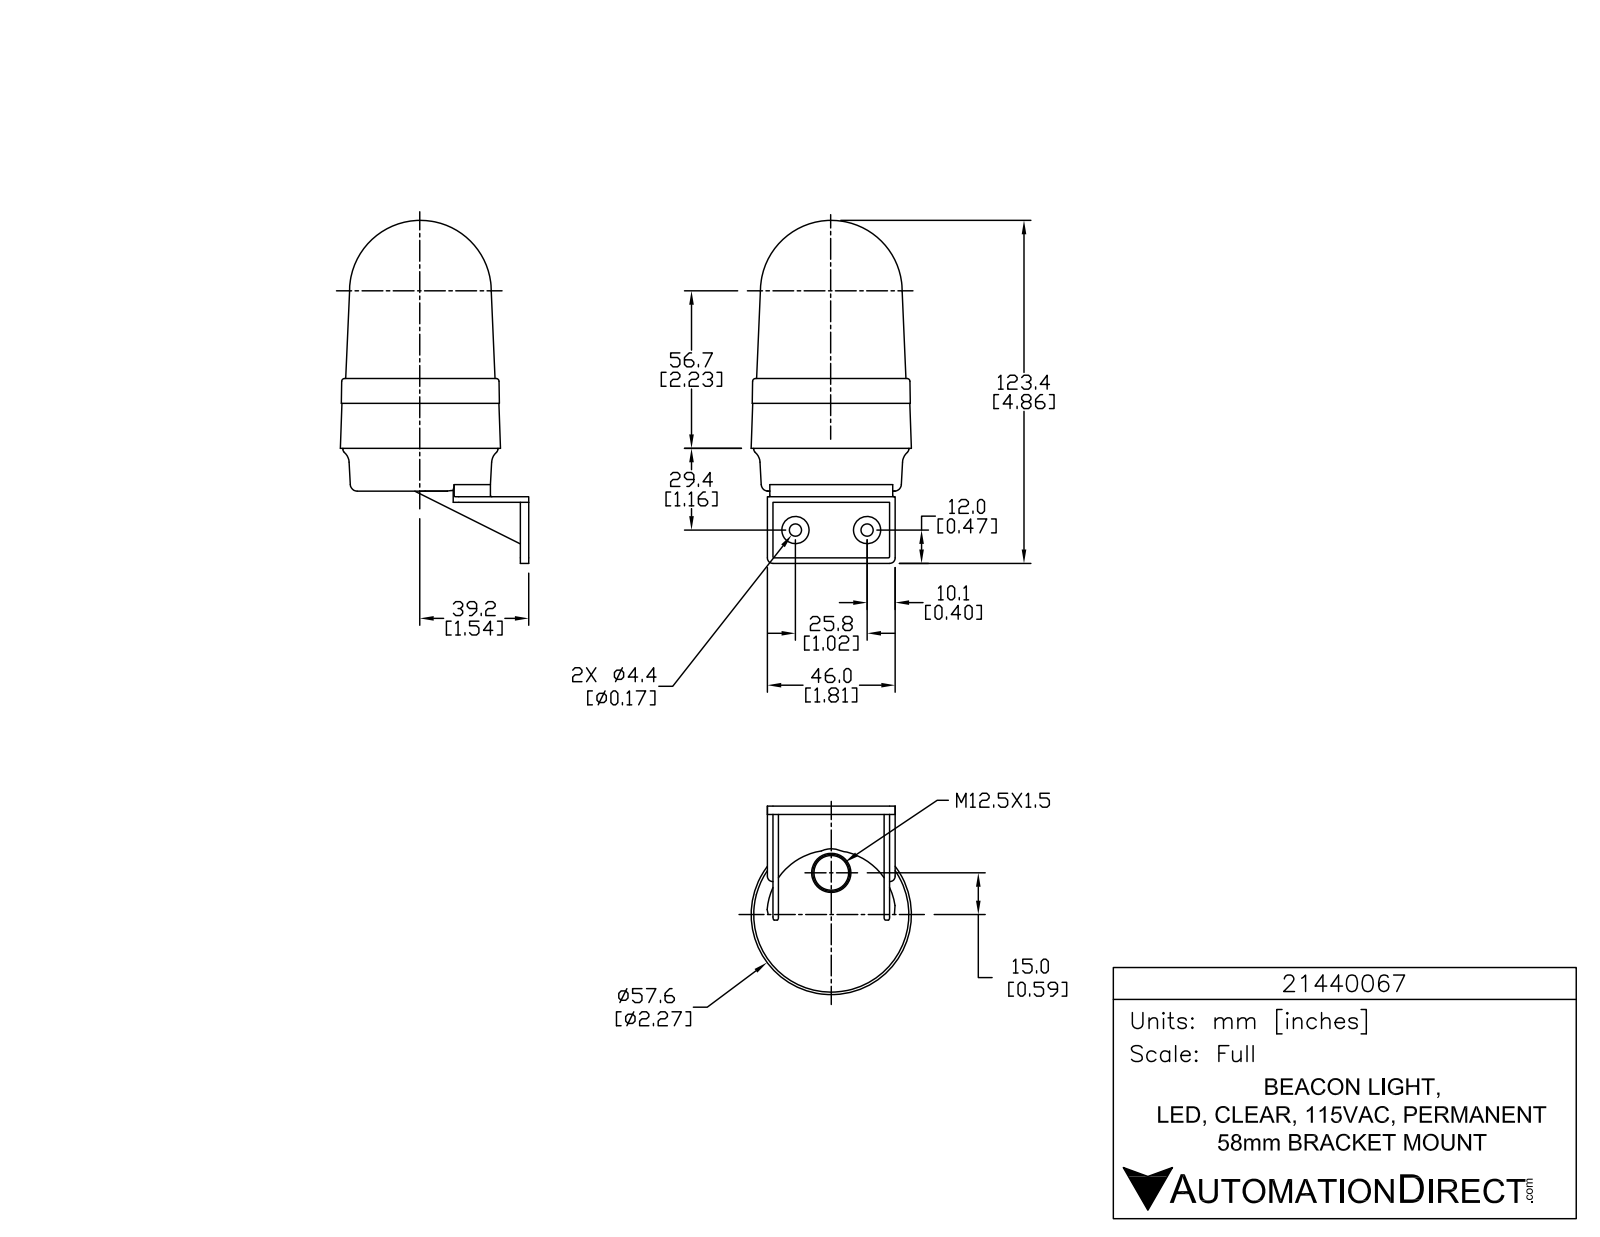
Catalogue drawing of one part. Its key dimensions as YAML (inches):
part_name: "21440067"
step_written_by: "SolidWorks 2015 (AUTOMOTIVE_DESIGN)"
units: inches
bodies: {solids: 1, faces: 828, planar: 551, cylindrical: 179, other: 98}
overall_size: [4.858, 2.852, 2.407]
volume: 12.43
surface_area: 37.49
round_holes:
  - {diameter: 0.039, count: 3}
  - {diameter: 0.173, count: 2}
round_bosses_or_shafts:
  - {diameter: 0.226, count: 3}
  - {diameter: 0.056, count: 3}
  - {diameter: 0.386, count: 2}
  - {diameter: 2.197, count: 1}
partial_cylinders:
  - {radius: 0.008, count: 6}
  - {radius: 0.008, count: 6}
  - {radius: 0.008, count: 6}
  - {radius: 0.02, count: 6}
  - {radius: 0.131, count: 6}
  - {radius: 0.079, count: 4}
  - {radius: 0.004, count: 3}
  - {radius: 0.005, count: 3}
face_to_face_distances: [0.079, 0.157, 1.575, 1.654, 0.039, 0.118, 1.496, 0.866, 0.945, 0.764]
hole_center_spacings: [1.016]
